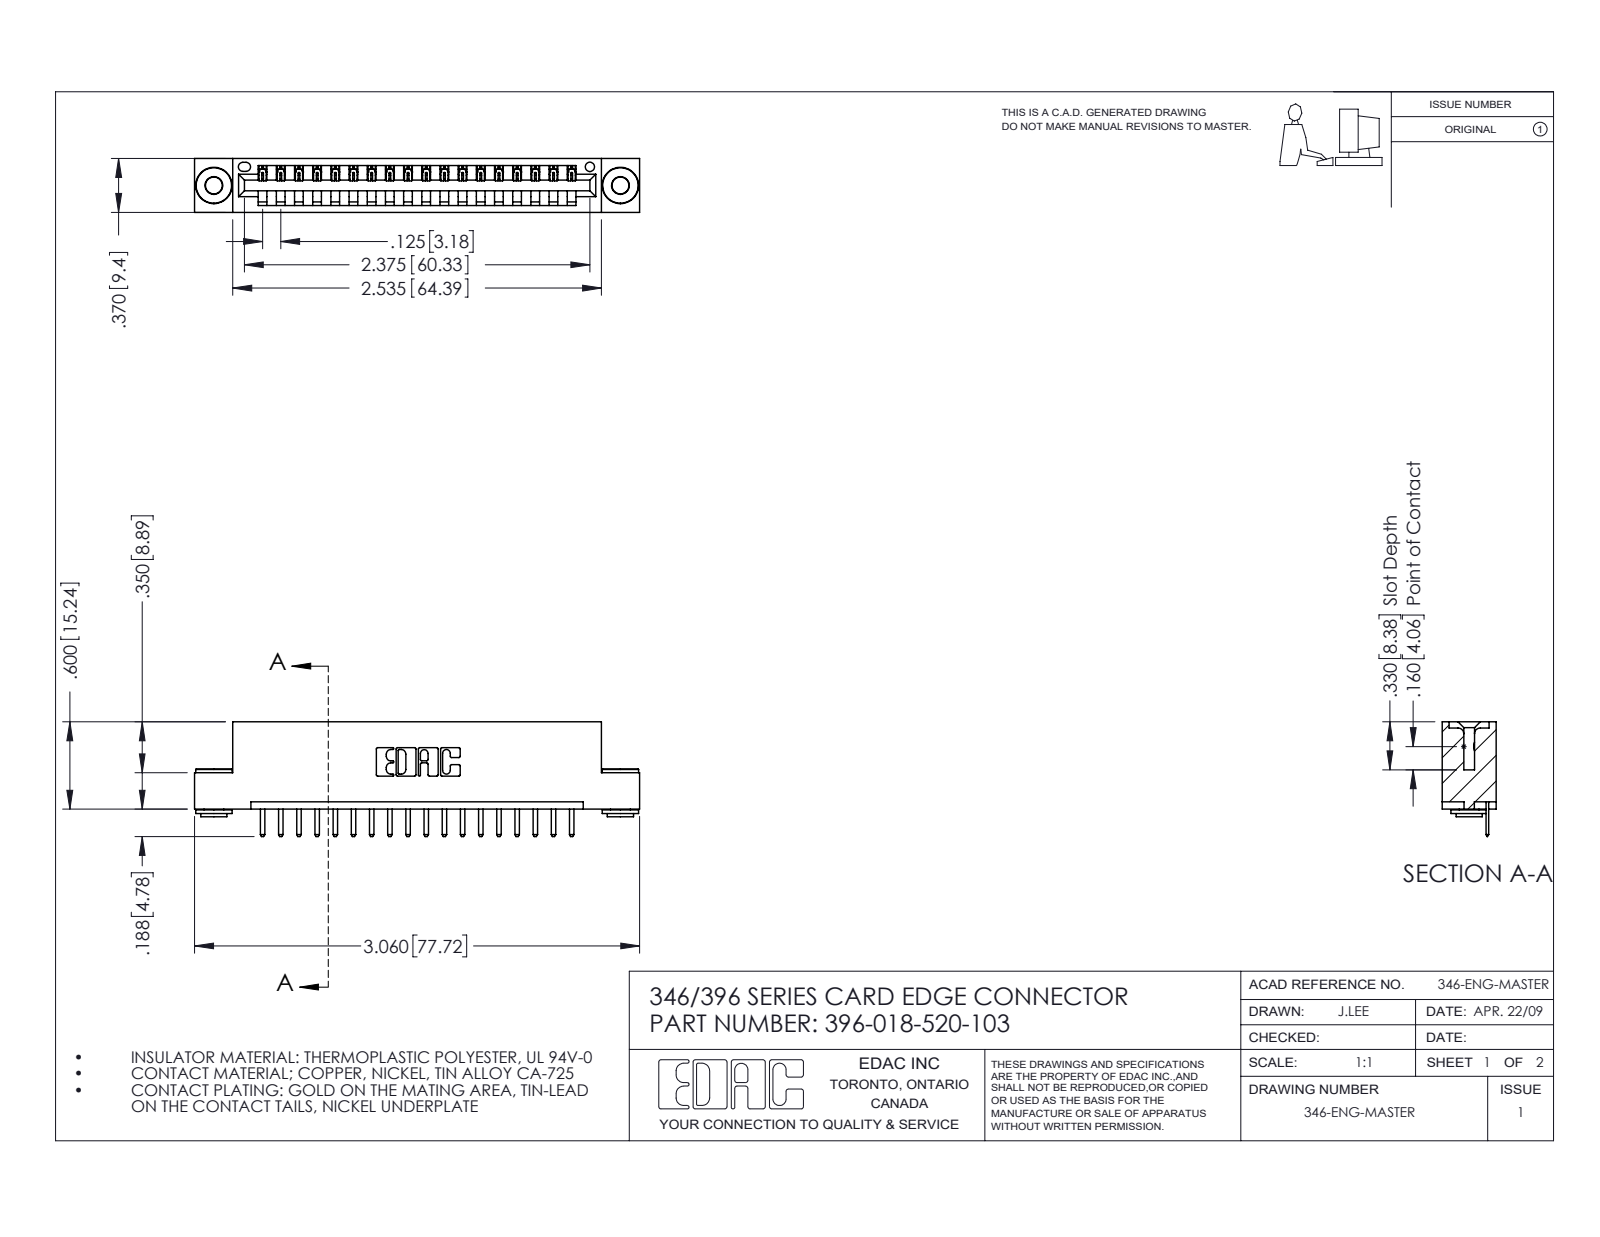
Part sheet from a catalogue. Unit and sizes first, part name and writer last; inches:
Units: inches
Overall size (bounding box): 3.06 × 0.788 × 0.37
Round holes (diameter × count): ⌀0.116 ×2, ⌀0.156 ×2, ⌀0.064 ×1
Round bosses / shafts (diameter × count): ⌀0.25 ×2, ⌀0.18 ×2, ⌀0.136 ×2
Partial cylindrical surfaces — rounded edges, fillets, slot ends (radius × count): R0.01 ×38, R0.006 ×36, R0.01 ×22, R0.007 ×6, R0.031 ×6, R0.026 ×3, R0.031 ×2, R0.04 ×2
Main face-to-face distances: 0.048, 0.322, 0.37, 0.25, 0.148, 0.222, 0.1, 0.174, 0.025, 0.072
Hole centre spacings: 0.246, 2.588, 2.795
Volume: 0.442 in³ · Surface area: 13.7 in²
Bodies: 21 solids, 1276 faces (842 planar, 426 cylindrical, 8 other)
Part name (STEP PRODUCT): 345-250-002_345-250-002-102; 346 Part_Flush Mounting Lugs - 0.156 Dia-TH; 345-292-001_345-293-120; 396-018-520-103
STEP written by: SolidWorks 2016 (CONFIG_CONTROL_DESIGN)
